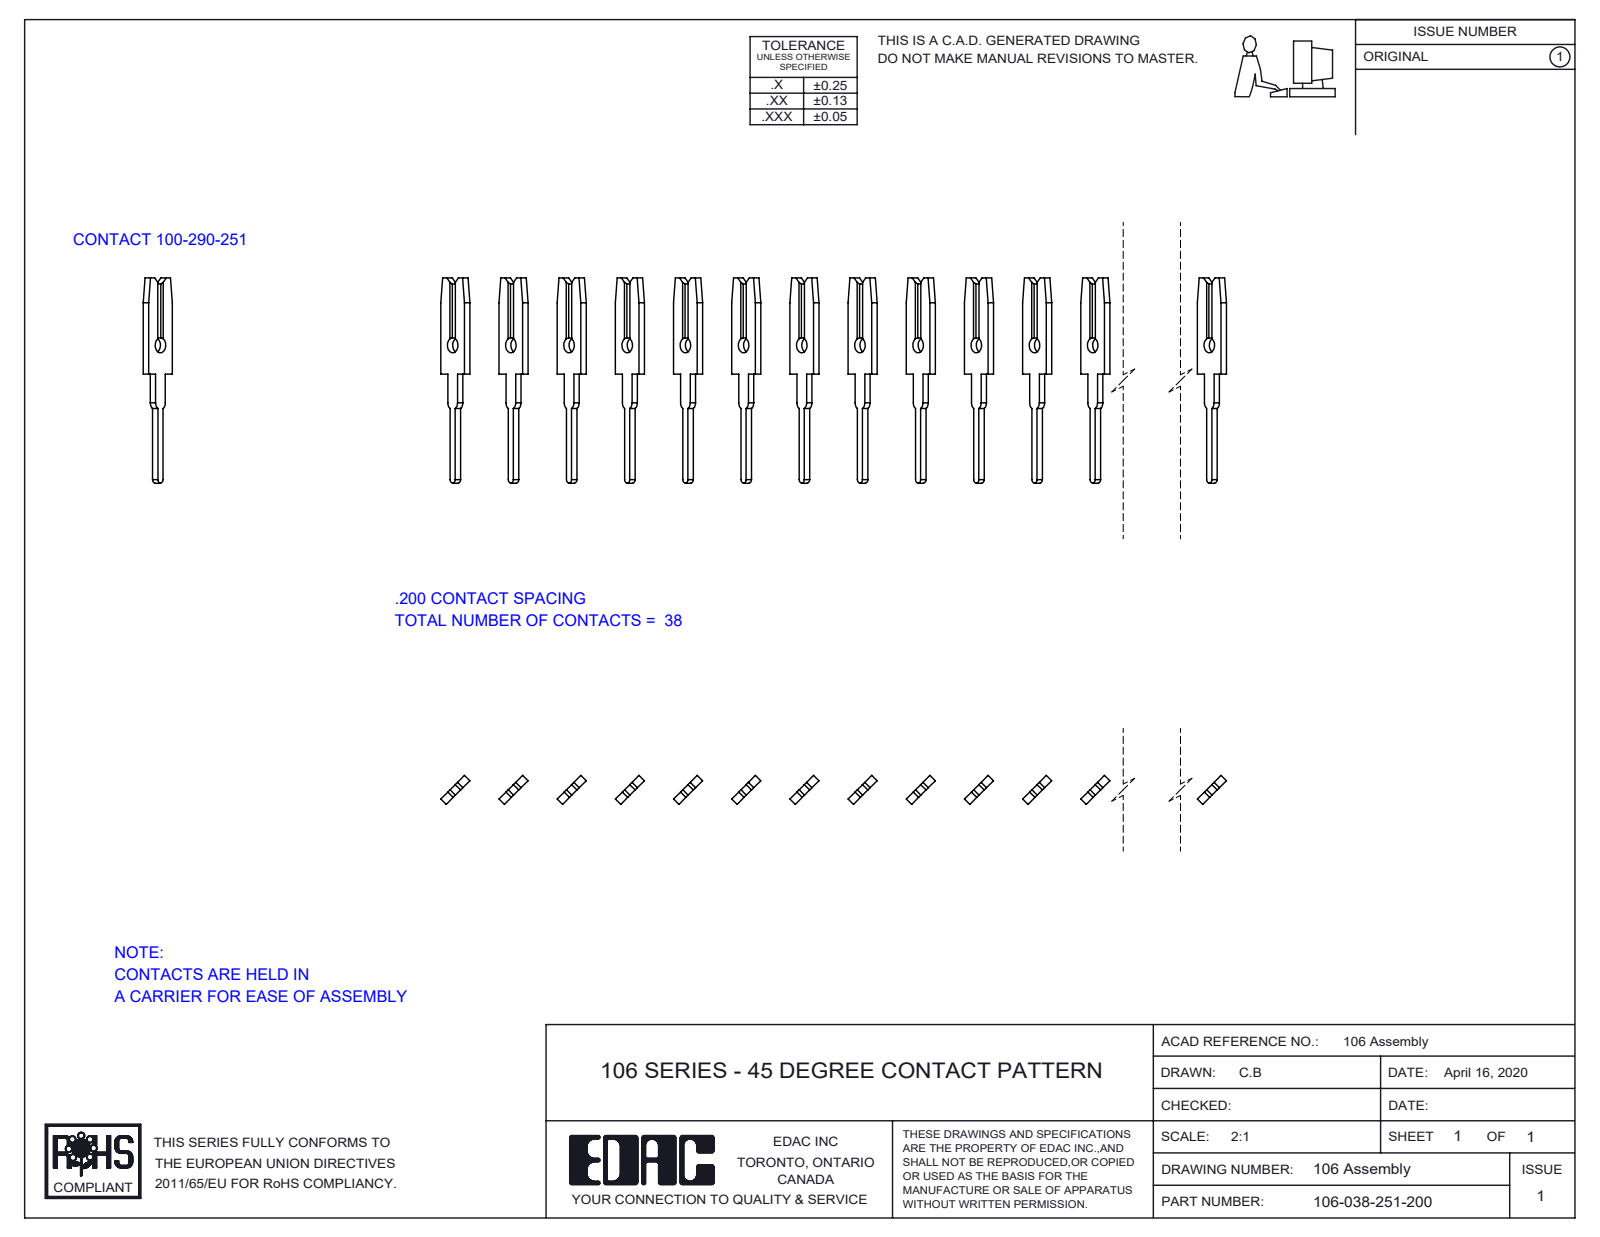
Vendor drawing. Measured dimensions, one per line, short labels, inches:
name: 106-038-251-200; 100-290-001_100-290-251
written by: SolidWorks 2016 (CONFIG_CONTROL_DESIGN)
unit: in
bodies: 38 solids, 1064 faces (836 planar, 228 cylindrical, 0 other)
size: 7.5 × 0.705 × 0.1
volume: 0.042 in³; area: 5.293 in²
holes: 38× ⌀0.052
rounds: 38× R0.012, 38× R0.024
face distances: 0.141, 0.848, 0.707, 0.283, 0.99, 0.566, 0.424, 1.131, 0.424, 1.556
hole spacings: 0.141, 0.283, 0.424, 0.848, 1.839, 0.99, 1.556, 1.697
